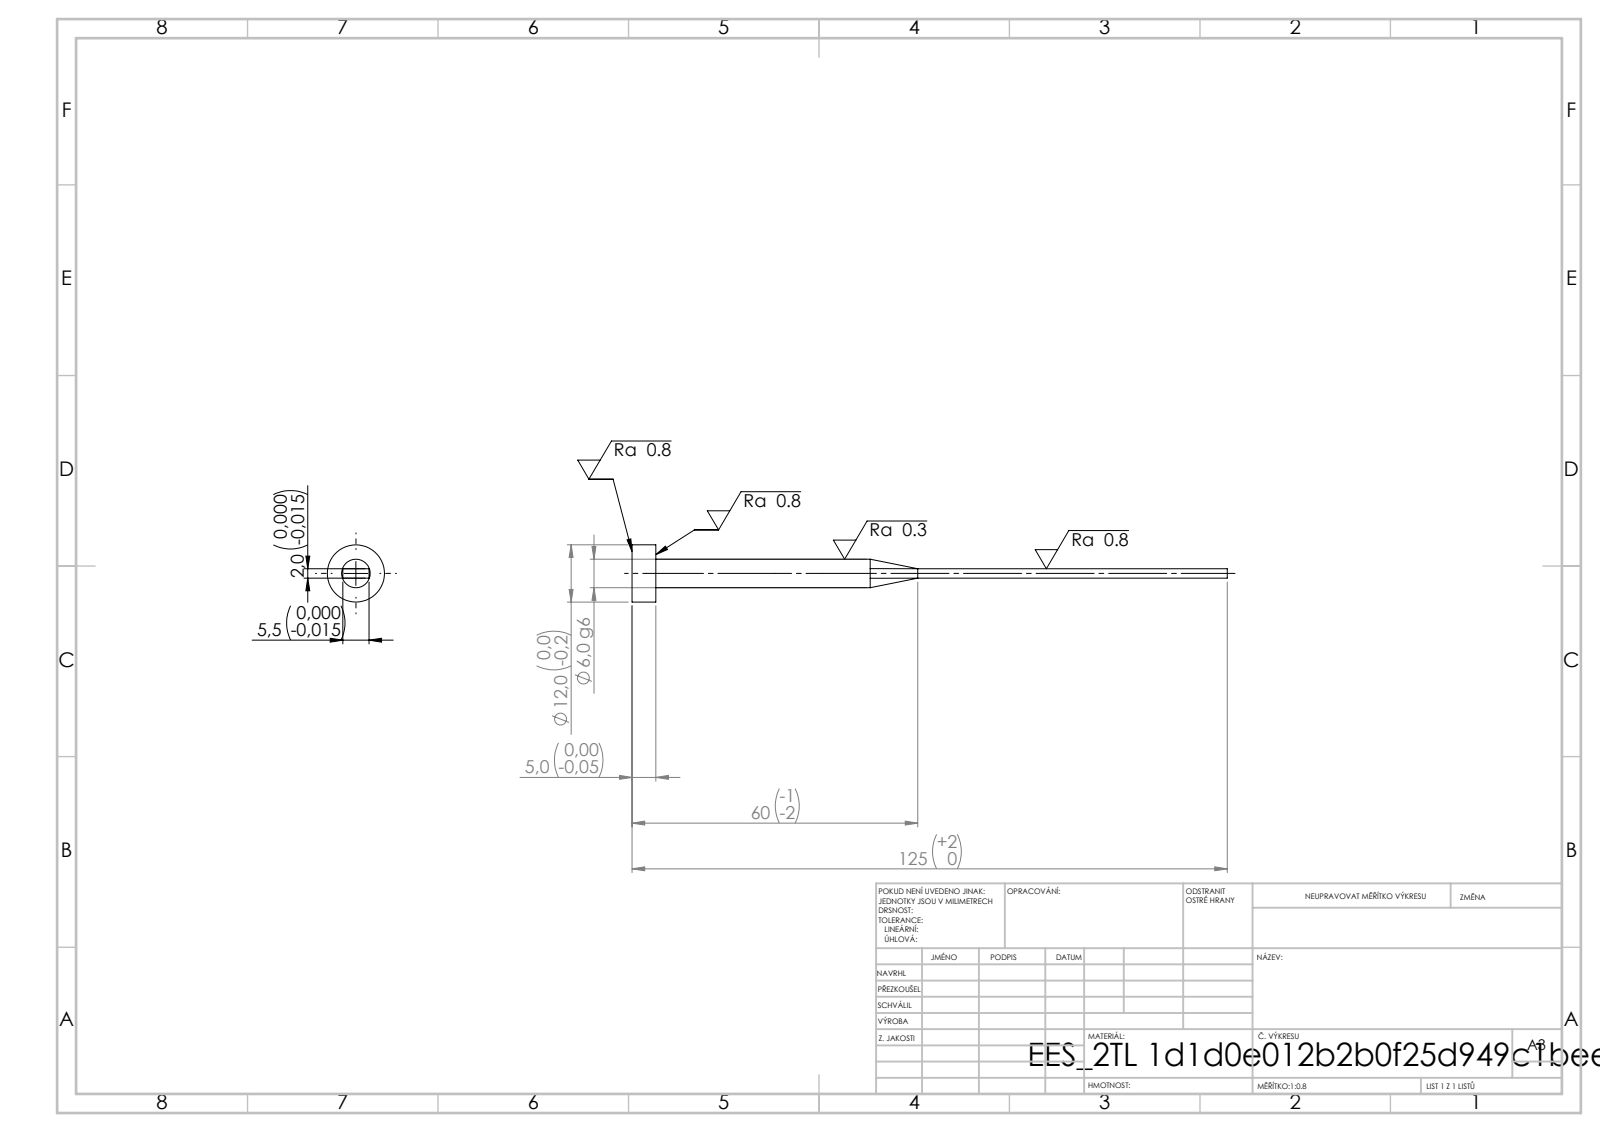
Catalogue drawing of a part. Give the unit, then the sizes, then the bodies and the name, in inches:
Units: inches
Overall size (bounding box): 4.921 × 0.472 × 0.472
Round bosses / shafts (diameter × count): ⌀0.472 ×1, ⌀0.236 ×1
Main face-to-face distances: 0.079, 0.217, 0.197, 4.921, 4.724
Volume: 0.167 in³ · Surface area: 3.698 in²
Bodies: 1 solid, 15 faces (7 planar, 4 cylindrical, 4 other)
STEP written by: SolidWorks 2019 (CONFIG_CONTROL_DESIGN)
